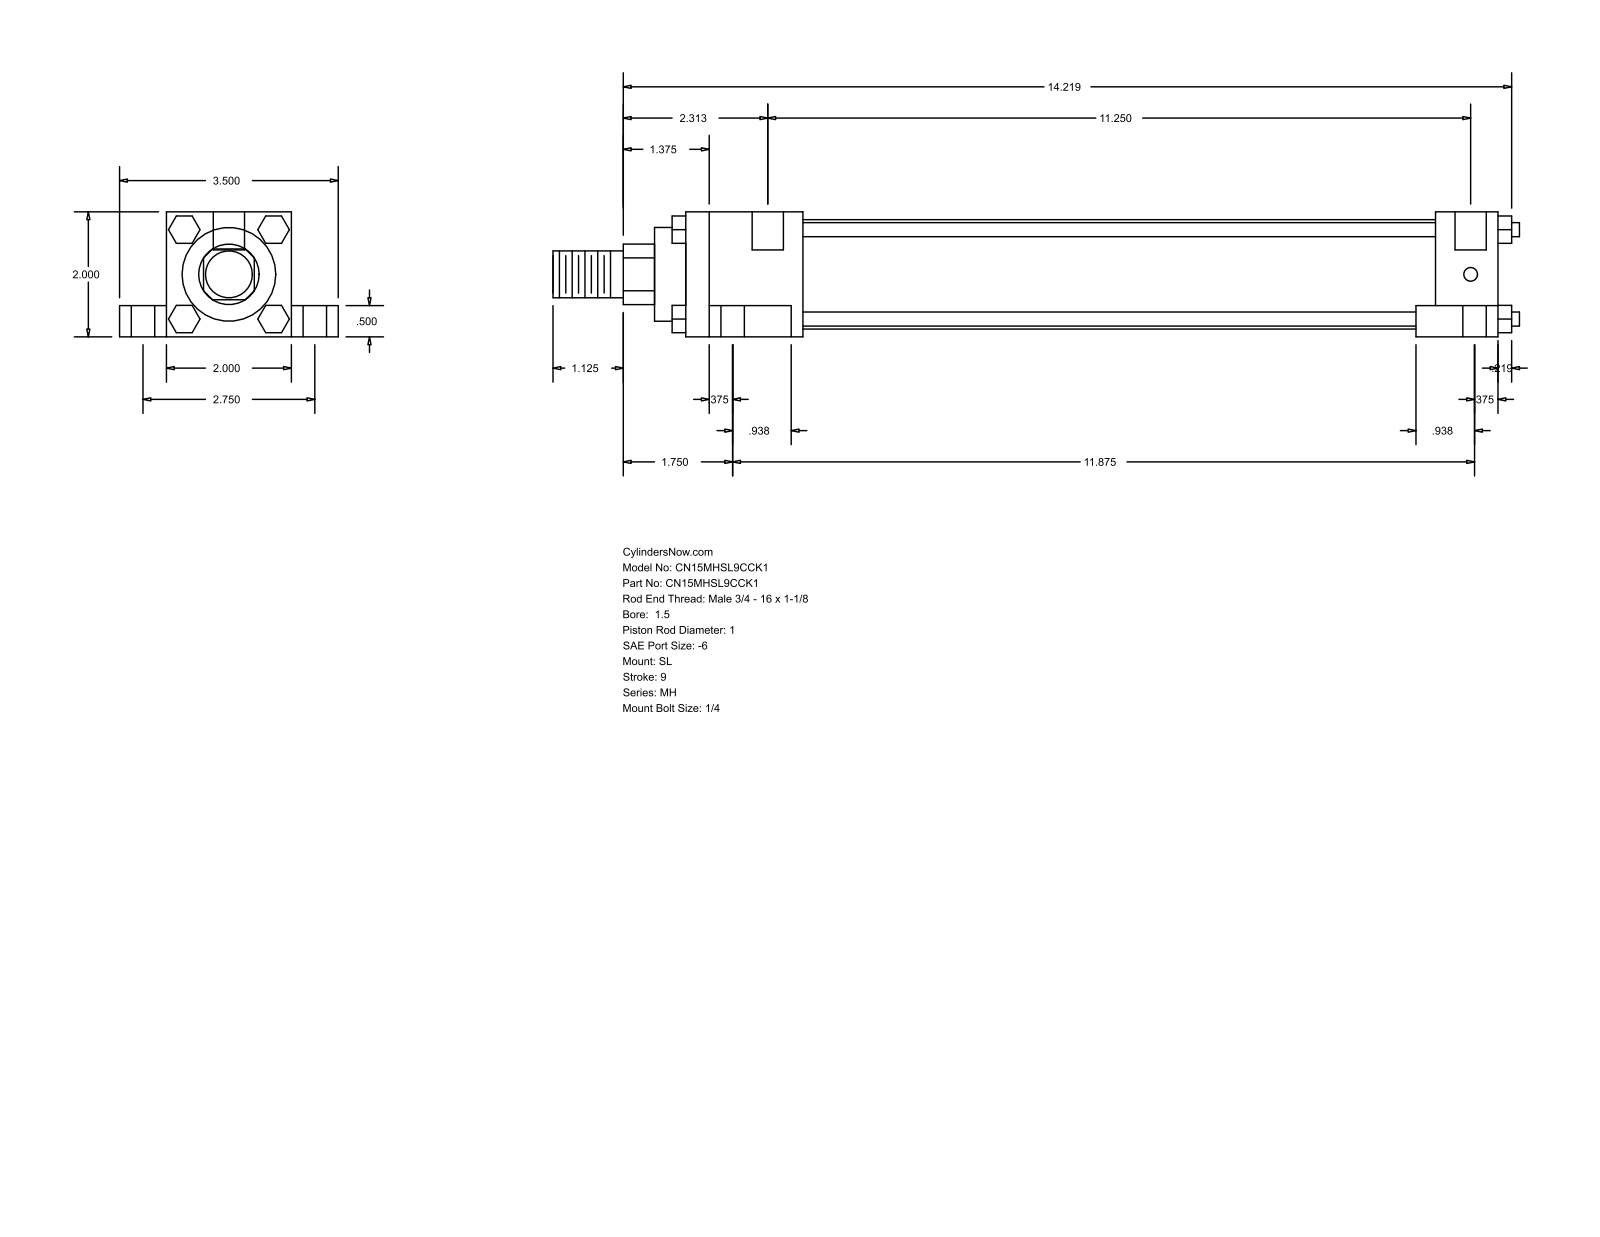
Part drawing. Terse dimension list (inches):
name: MH_SL__0150_1
written by: GSSL Pune (CONFIG_CONTROL_DESIGN)
unit: in
bodies: 0 solids, 148 faces (112 planar, 36 cylindrical, 0 other)
size: 15.469 × 3.5 × 2
holes: 4× ⌀0.219, 4× ⌀0.375, 4× ⌀0.625, 2× ⌀0.5
bosses: 4× ⌀0.225, 1× ⌀1.75, 1× ⌀1.5, 1× ⌀1, 1× ⌀0.75
rounds: 1× R0.484
face distances: 2, 0.5, 1.5, 0.75, 2.75, 13, 1, 0.375, 1.313, 11.313
hole spacings: 1.376, 1.443, 1.485, 2.75, 11.375, 11.395, 11.52, 11.875
